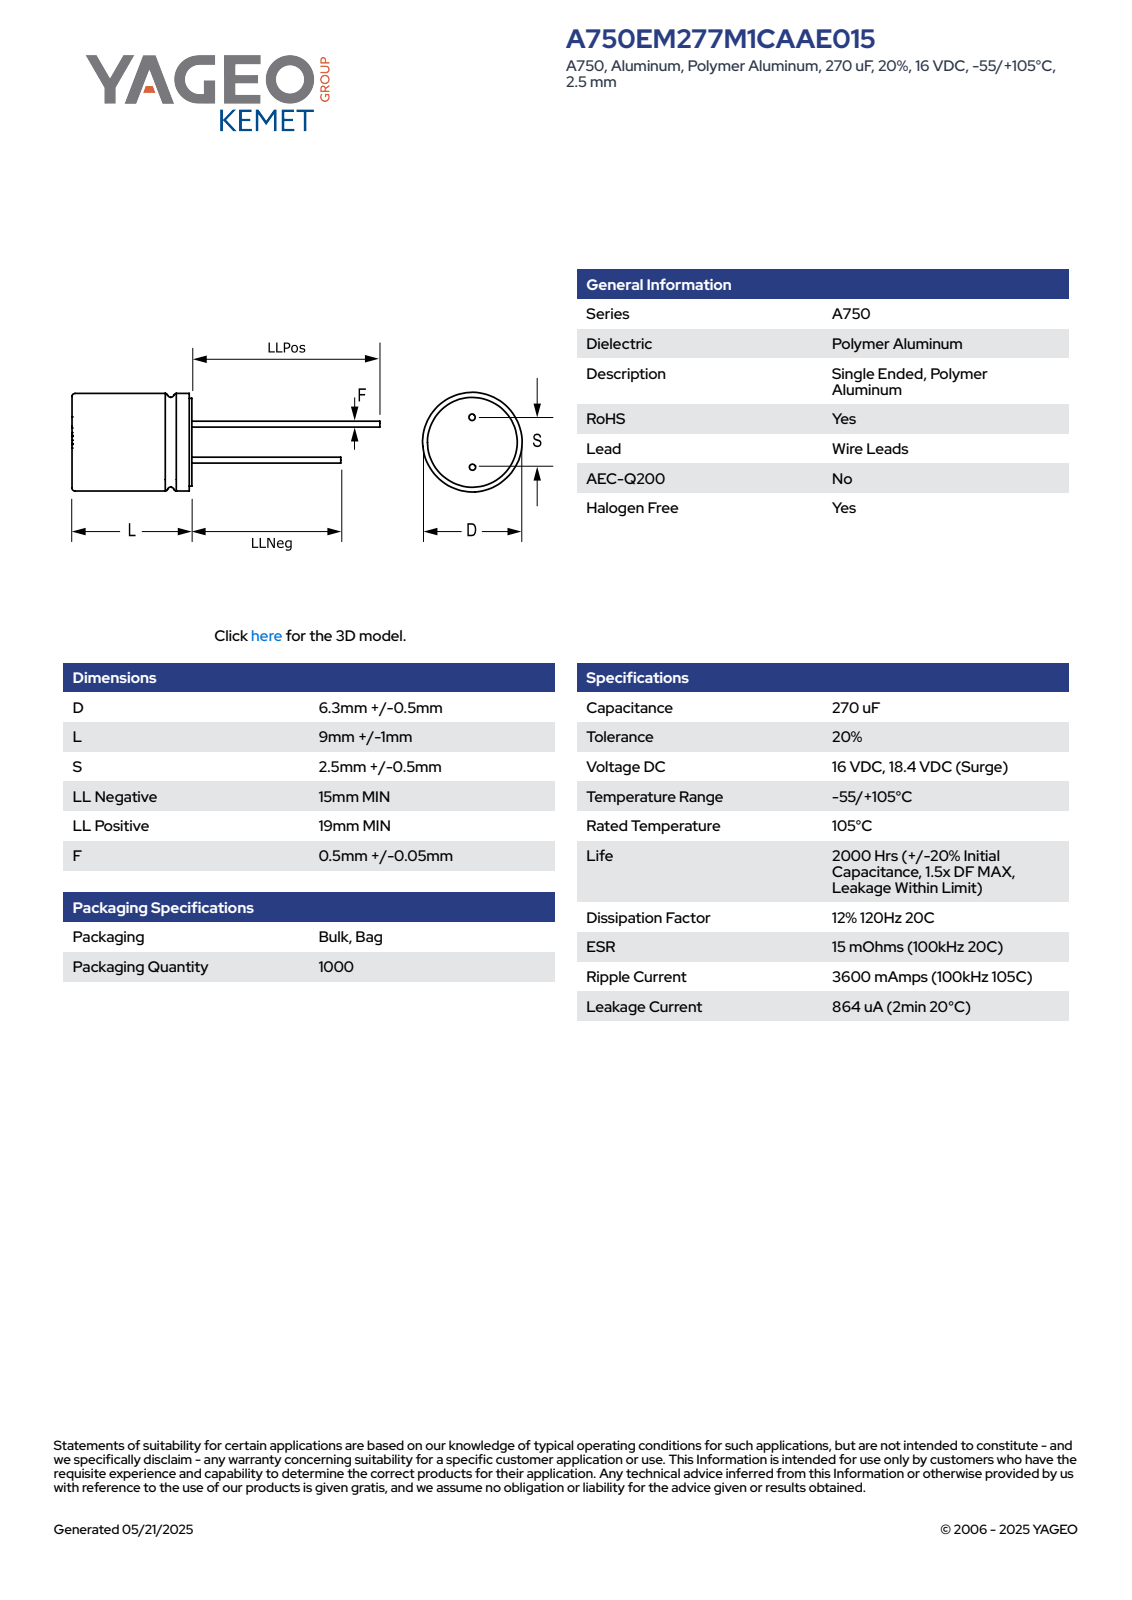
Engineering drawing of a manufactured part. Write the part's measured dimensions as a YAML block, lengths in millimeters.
part_name: "CAR_KP_6.3X9_D6.8L10S2.5F0.55"
step_written_by: "SolidWorks 2014 (AUTOMOTIVE_DESIGN)"
units: millimeters
bodies: {solids: 4, faces: 75, planar: 61, cylindrical: 8, other: 6}
overall_size: [29, 6.8, 6.8]
volume: 368
surface_area: 353
round_bosses_or_shafts:
  - {diameter: 0.55, count: 2}
  - {diameter: 6.8, count: 1}
face_to_face_distances: [10, 10.01, 25.01, 29.01, 25, 29, 15, 19, 4, 0.75]
